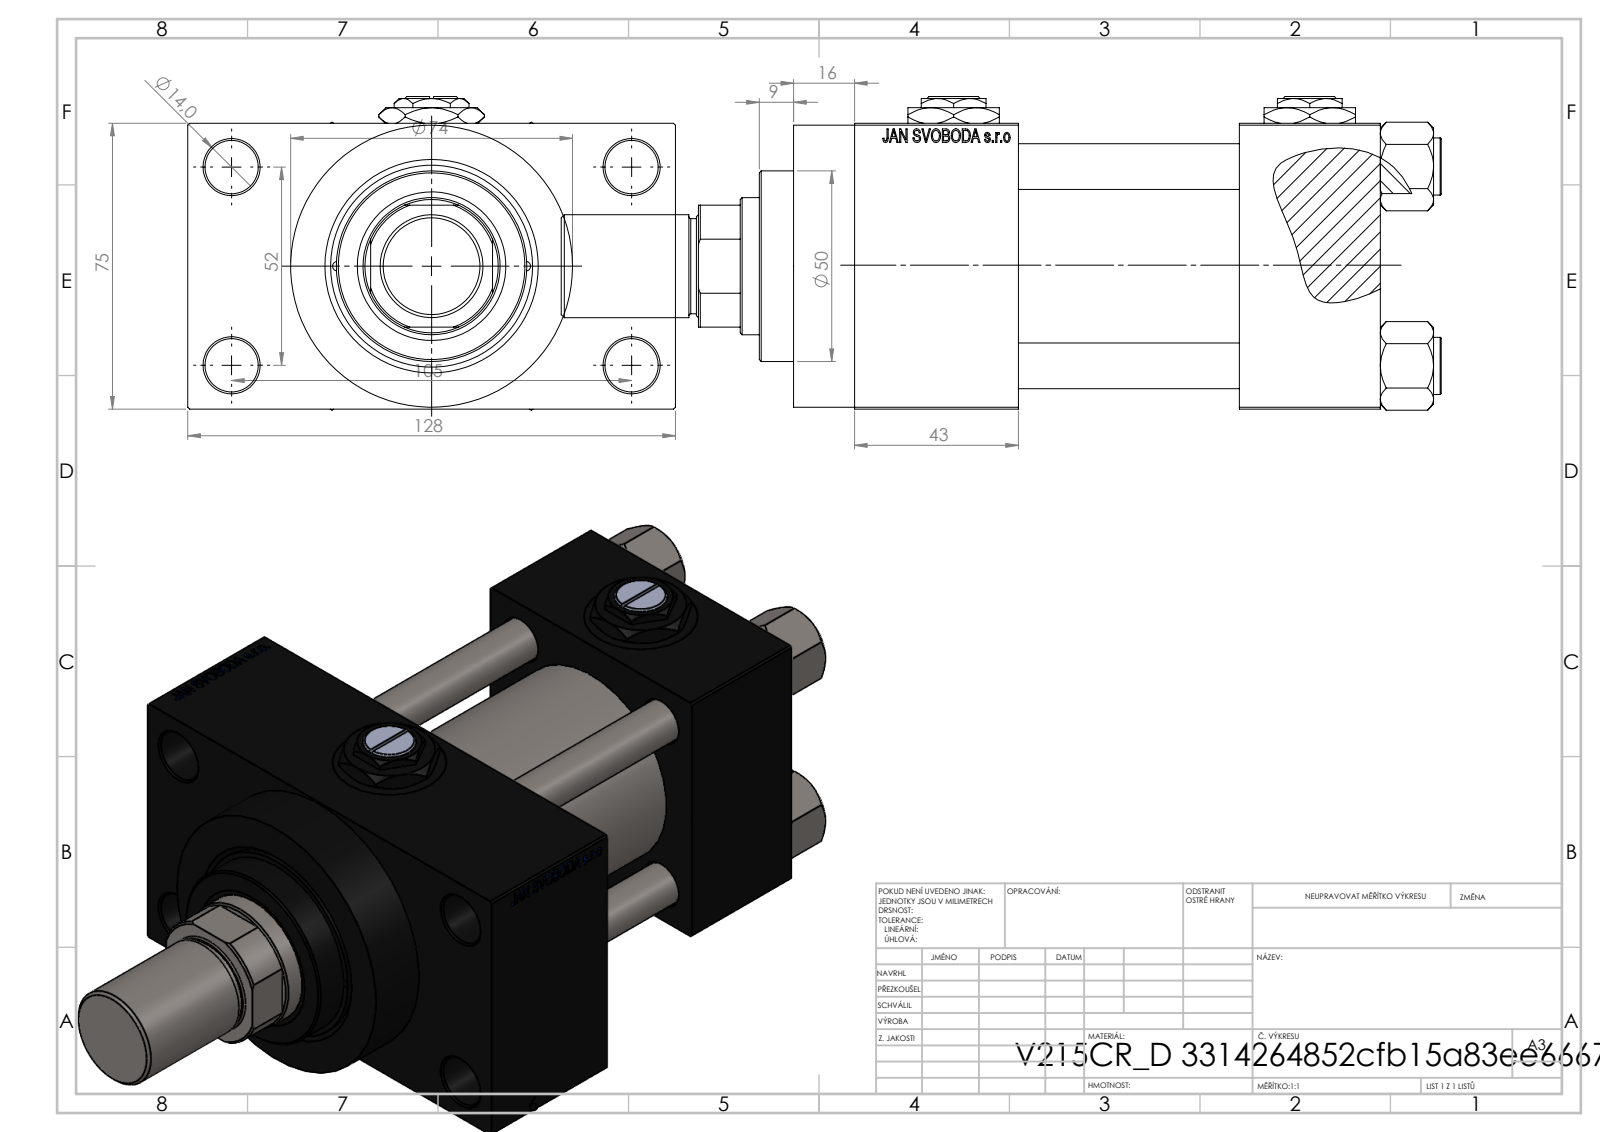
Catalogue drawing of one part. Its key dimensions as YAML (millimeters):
part_name: "Zatka_pro_OIL_PORT; V215CR_VCP_D; V215CR_D_Body; V215CR_D_TYCINKA (+3 more)"
step_written_by: "SolidWorks 2019 (CONFIG_CONTROL_DESIGN)"
units: millimeters
bodies: {solids: 14, faces: 1228, planar: 553, cylindrical: 107, other: 568}
overall_size: [231, 128, 82.27]
volume: 833102
surface_area: 183980
round_holes:
  - {diameter: 12, count: 4}
  - {diameter: 14, count: 4}
  - {diameter: 20.96, count: 4}
  - {diameter: 30, count: 4}
  - {diameter: 7, count: 3}
  - {diameter: 2.5, count: 2}
  - {diameter: 25.5, count: 1}
  - {diameter: 36, count: 1}
  - {diameter: 39, count: 1}
  - {diameter: 41, count: 1}
  - {diameter: 53, count: 1}
round_bosses_or_shafts:
  - {diameter: 15, count: 4}
  - {diameter: 74, count: 1}
  - {diameter: 56, count: 1}
  - {diameter: 50, count: 1}
  - {diameter: 27, count: 1}
  - {diameter: 25, count: 1}
partial_cylinders:
  - {radius: 17.5, count: 1}
face_to_face_distances: [75, 58, 37, 95, 26.5, 138, 43, 101, 101.5, 16]
hole_center_spacings: [26.19, 26.35, 36.98, 38.03, 52.3, 57.22, 58.43, 58.59]
